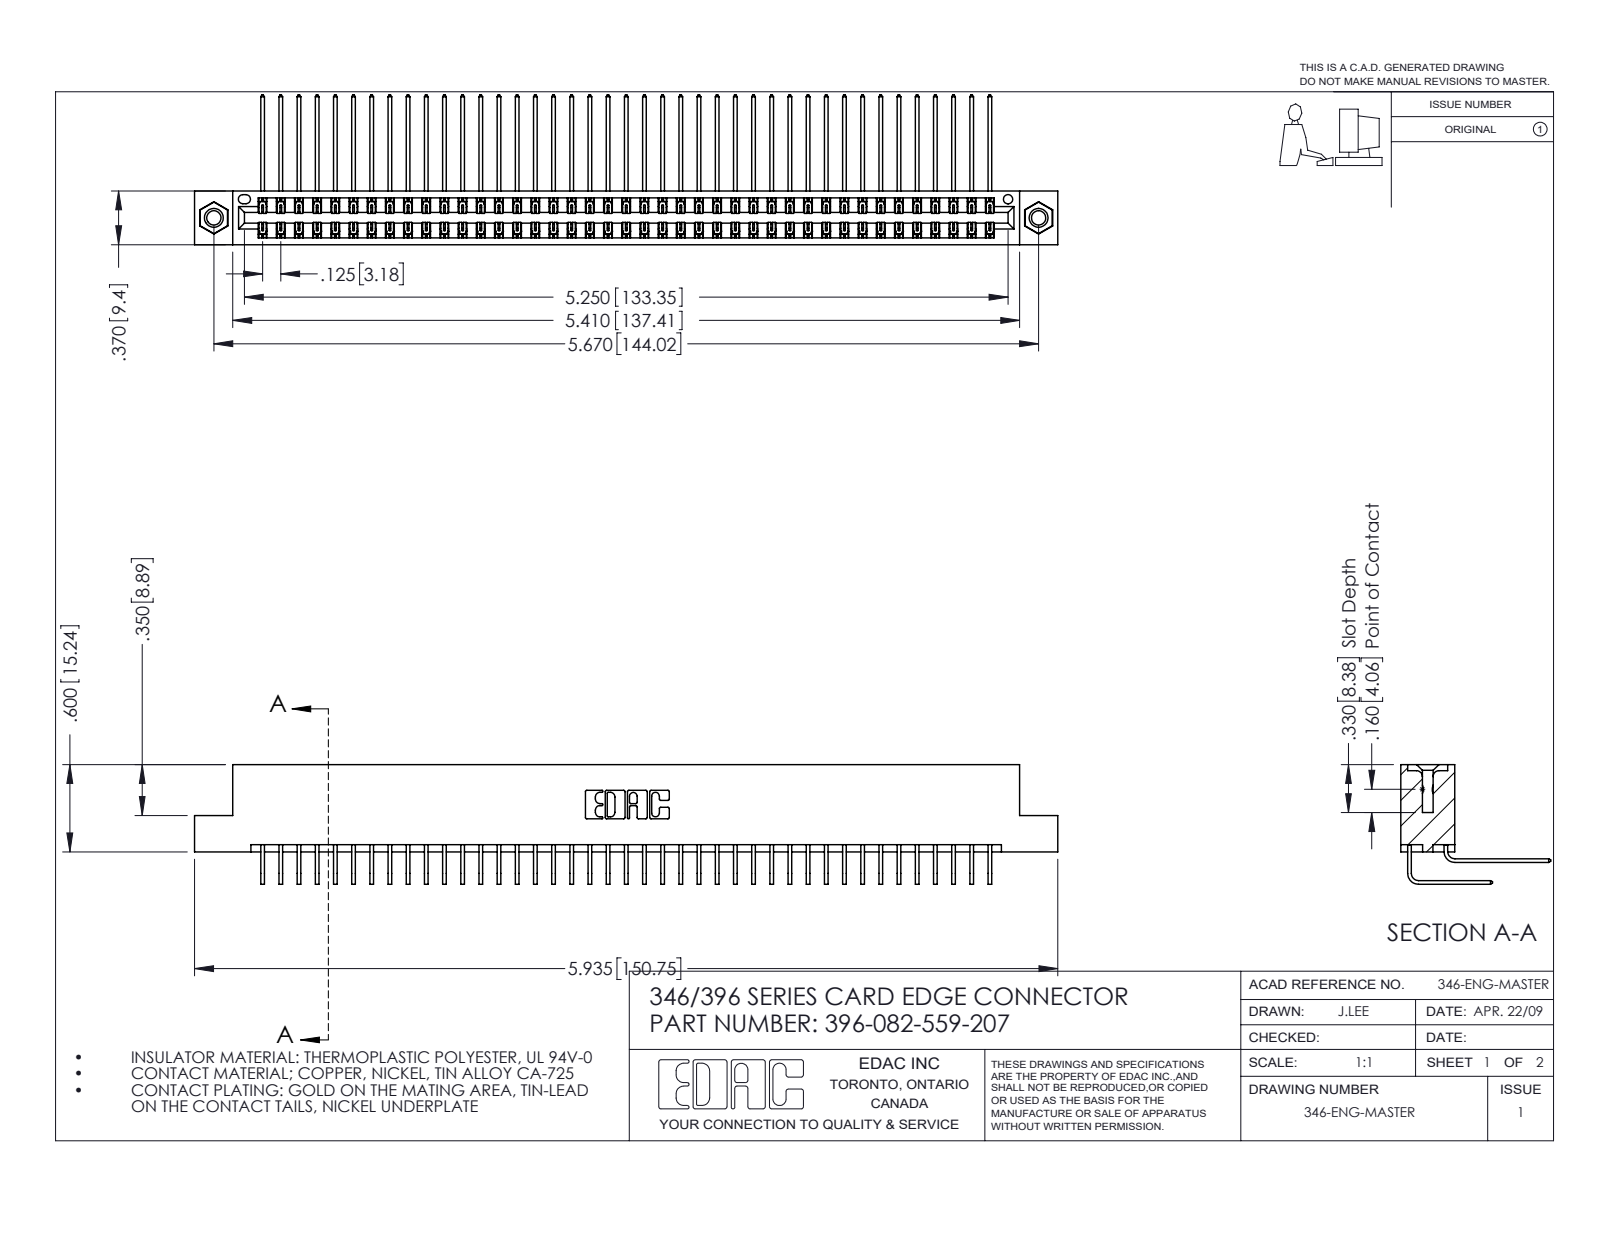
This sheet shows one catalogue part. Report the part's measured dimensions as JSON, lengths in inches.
{"part_name": "345-292-001_559 Tail - 2; 346 Part_Flush Mounting Lugs - 0.156 Dia-TI; 396-082-559-207; 345-292-001_558 559 Tail - 1 (+1 more)", "step_written_by": "SolidWorks 2016 (CONFIG_CONTROL_DESIGN)", "units": "inches", "bodies": {"solids": 85, "faces": 4610, "planar": 3142, "cylindrical": 1452, "other": 16}, "overall_size": [5.935, 1.03, 0.823], "volume_in3": 0.925, "surface_area_in2": 35.83, "round_holes": [[0.098, 2], [0.125, 2], [0.156, 2], [0.064, 1]], "round_bosses_or_shafts": [[0.155, 2]], "partial_cylinders_radius": [[0.006, 123], [0.01, 22], [0.007, 6], [0.031, 6], [0.026, 3], [0.014, 2], [0.022, 2], [0.024, 2]], "face_to_face_distances": [0.048, 0.322, 0.025, 0.37, 0.072, 0.25, 0.298, 0.275, 0.148, 0.222], "hole_center_spacings": [0.246, 5.461, 5.67]}
